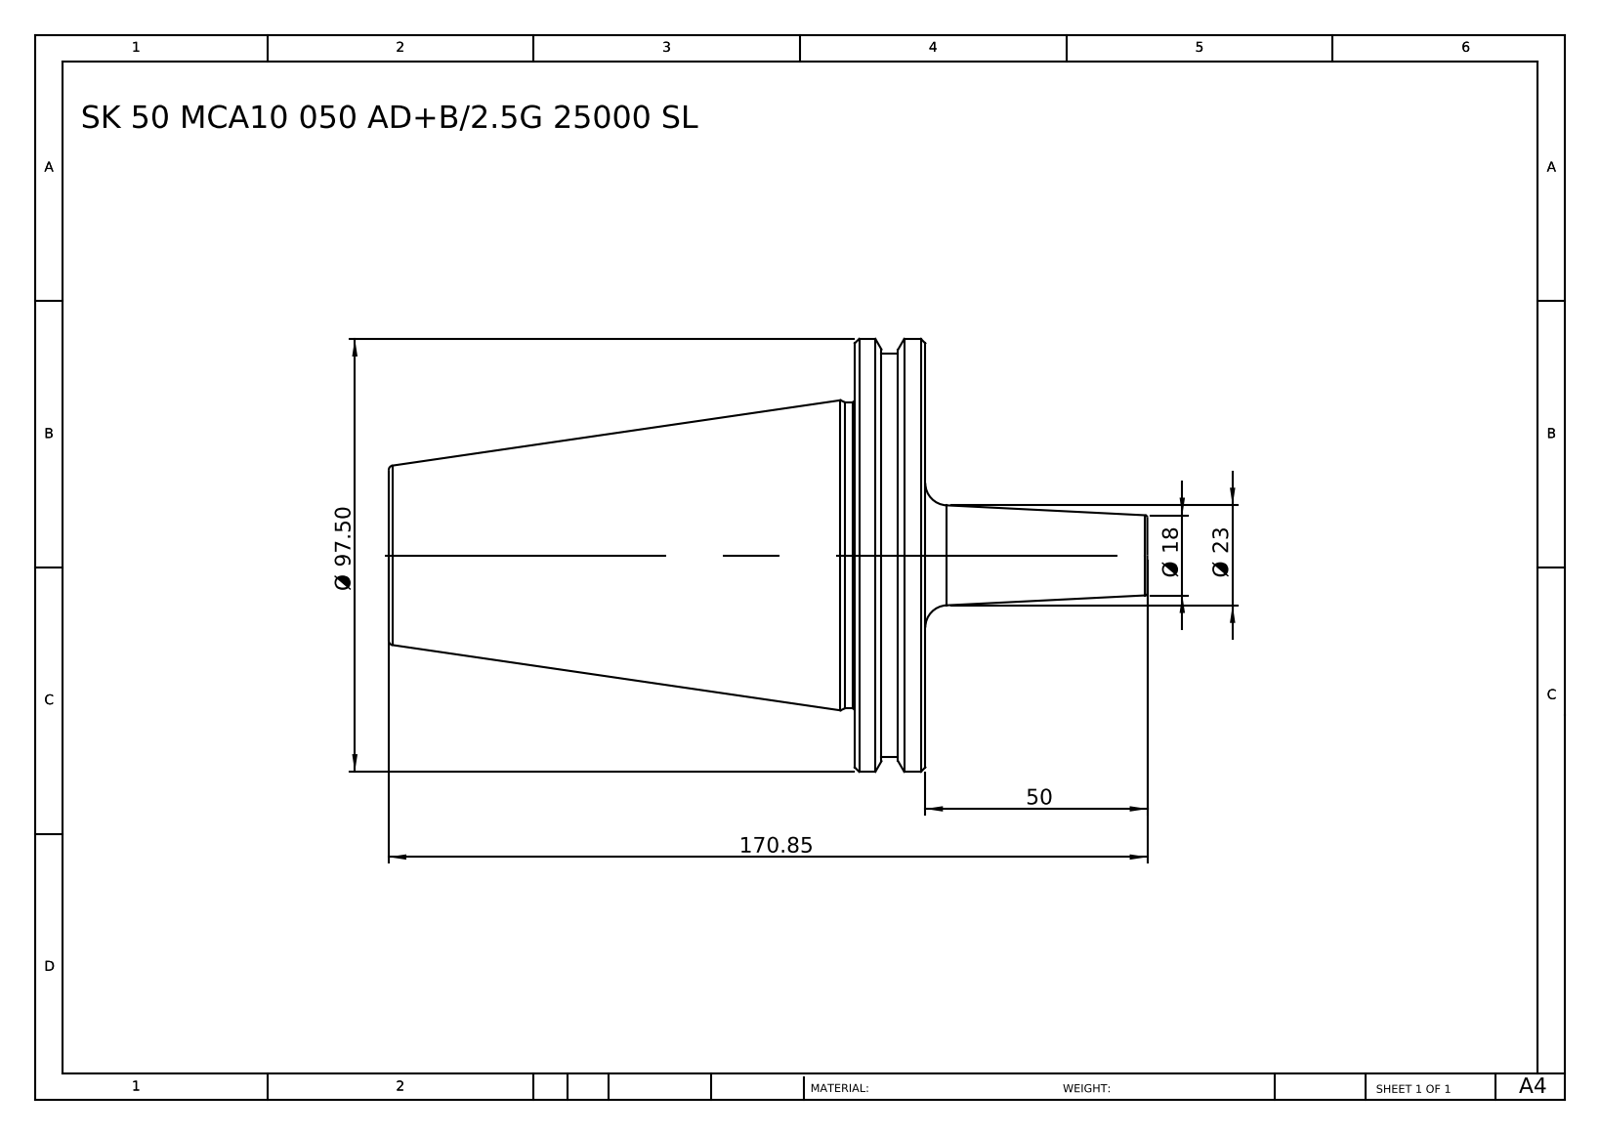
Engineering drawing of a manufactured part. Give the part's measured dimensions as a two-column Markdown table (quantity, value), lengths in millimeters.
| quantity | value |
| --- | --- |
| part name | SK 50 MCA10 050 AD+B-2.5G25000 SL |
| STEP written by | SolidWorks 2014 (CONFIG_CONTROL_DESIGN) |
| units | millimeters |
| bodies | 1 solid, 36 faces (6 planar, 8 cylindrical, 22 other) |
| overall size | 170.85 × 97.5 × 97.5 |
| volume | 390 491 mm³ |
| surface area | 39 526 mm² |
| round bosses / shafts (diameter × count) | 97.5 × 1, 91 × 1, 69 × 1 |
| main face-to-face distances | 15.9, 120.85, 104.95, 6.13, 9.88, 3.75, 9.77, 114.72, 6.02, 110.97 |
